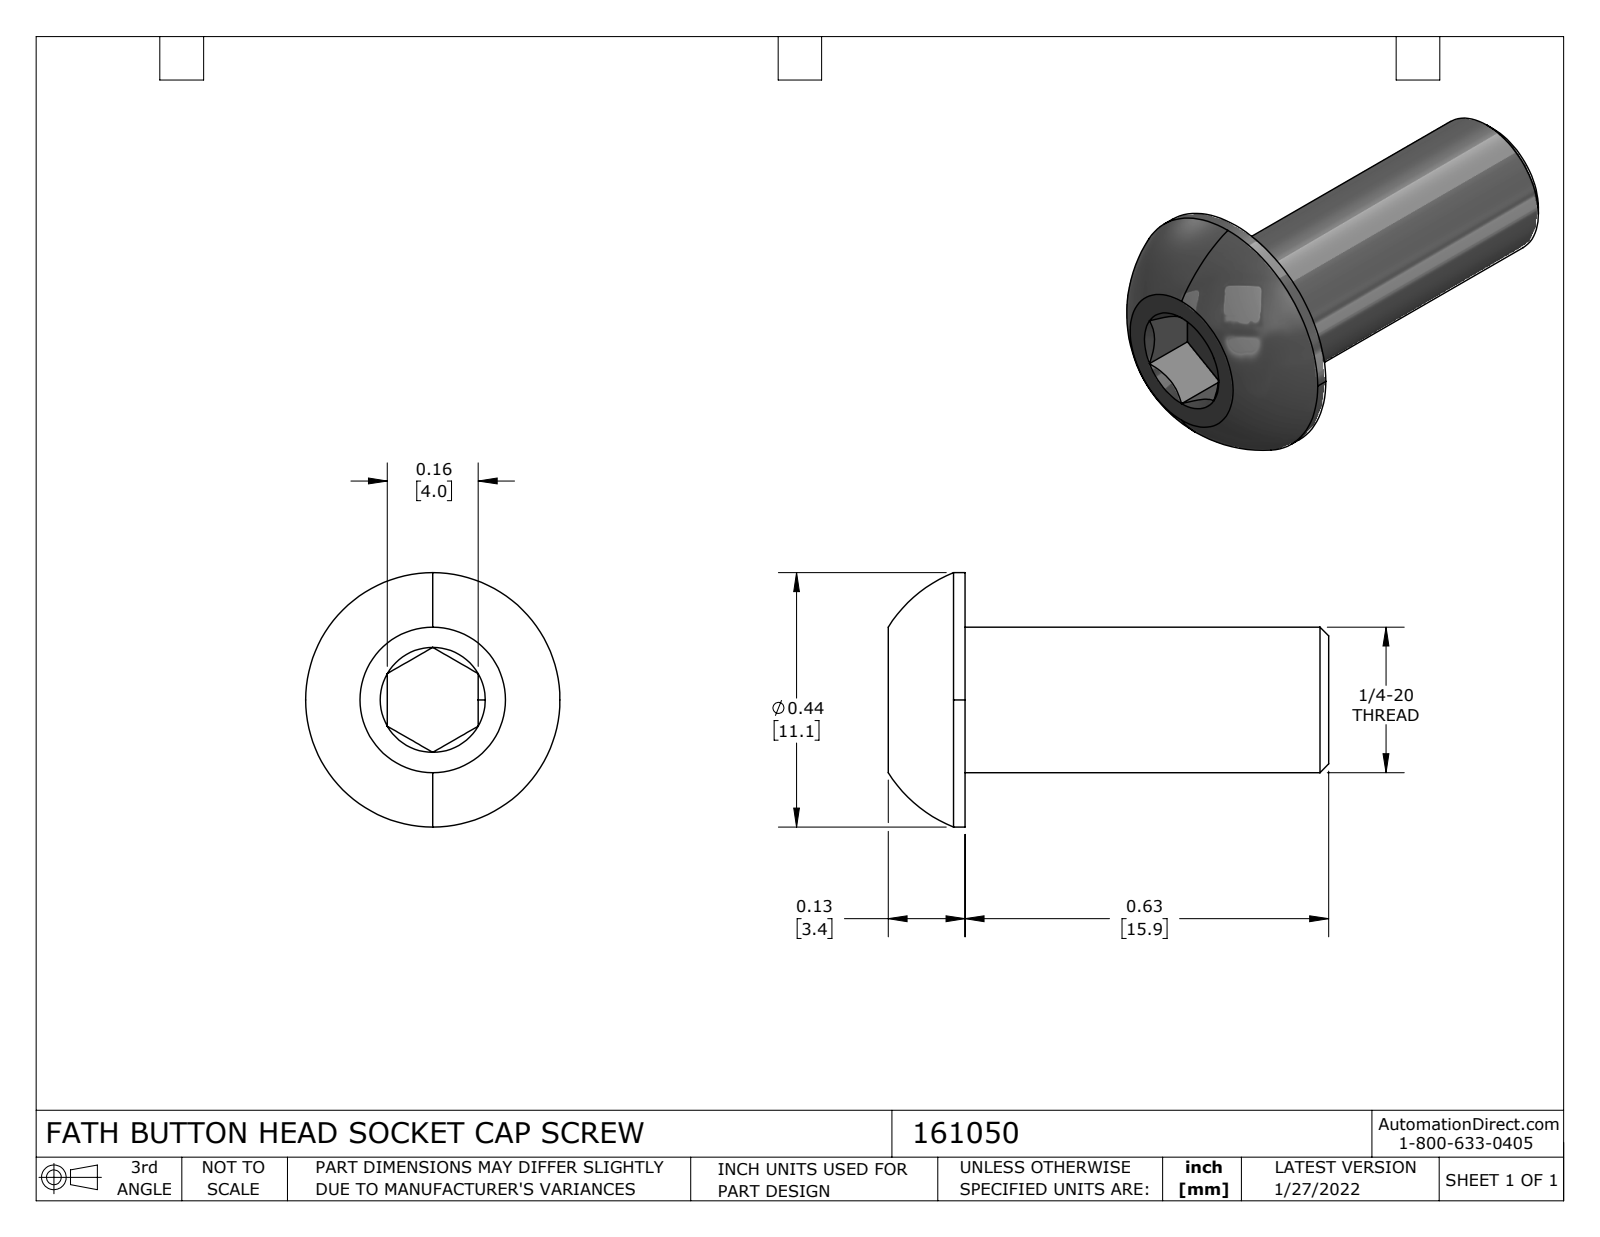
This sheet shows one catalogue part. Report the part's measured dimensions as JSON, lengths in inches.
{"part_name": "161050", "step_written_by": "SolidWorks 2021 (CONFIG_CONTROL_DESIGN)", "units": "inches", "bodies": {"solids": 1, "faces": 29, "planar": 12, "cylindrical": 4, "other": 13}, "overall_size": [0.757, 0.437, 0.437], "volume_in3": 0.043, "surface_area_in2": 0.929, "round_bosses_or_shafts": [[0.437, 1], [0.25, 1]], "face_to_face_distances": [0.625, 0.757, 0.132, 0.665, 0.039, 0.093, 0.156, 0.078]}
